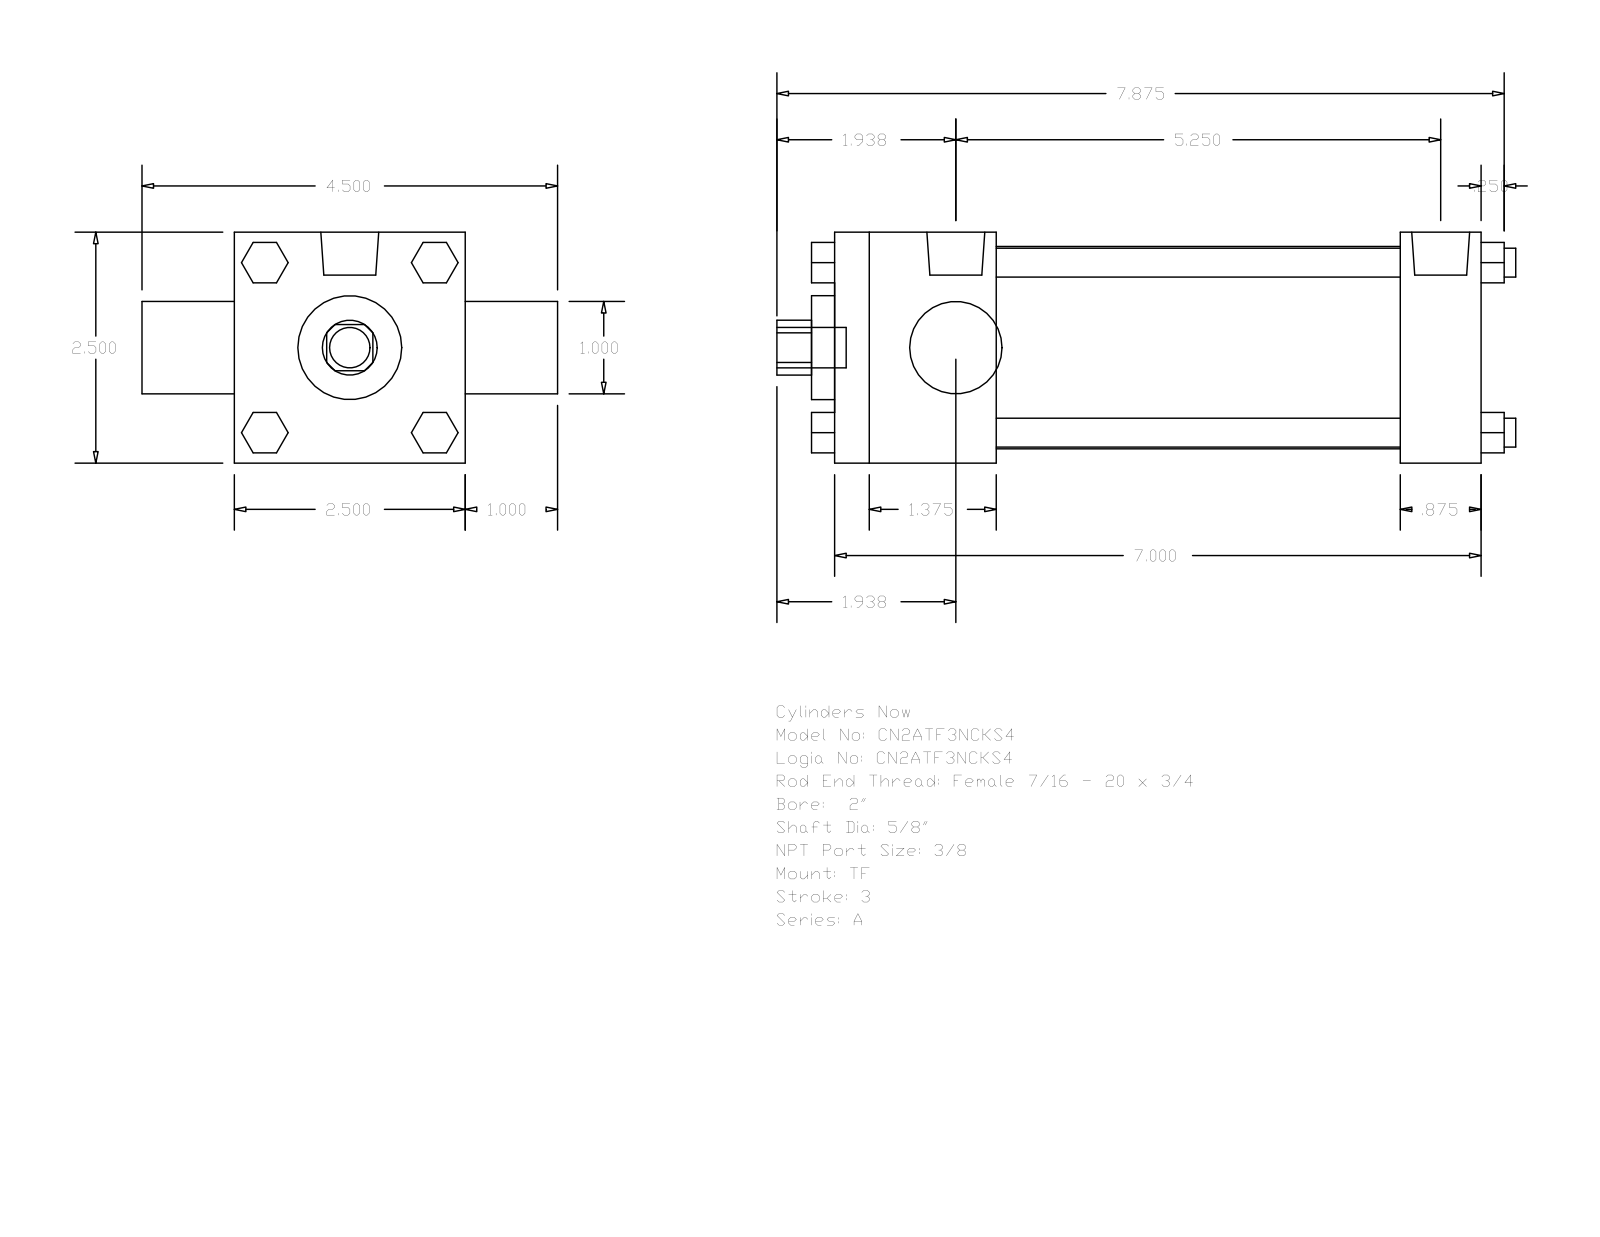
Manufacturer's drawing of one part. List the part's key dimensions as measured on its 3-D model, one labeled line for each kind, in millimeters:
Part name (STEP PRODUCT): A_TF__0200_0.625
STEP written by: GSSL Pune (CONFIG_CONTROL_DESIGN)
Units: millimetres
Bodies: 0 solids, 120 faces (92 planar, 28 cylindrical, 0 other)
Overall size (bounding box): 203.2 × 114.3 × 63.5
Round holes (diameter × count): ⌀15.88 ×1, ⌀25.4 ×1, ⌀28.57 ×1, ⌀55.63 ×1
Round bosses / shafts (diameter × count): ⌀7.94 ×4, ⌀5.56 ×3, ⌀15.93 ×2, ⌀11.11 ×1
Partial cylindrical surfaces — rounded edges, fillets, slot ends (radius × count): R7.54 ×1
Main face-to-face distances: 63.5, 177.8, 44.45, 155.57, 111.12, 133.35, 22.23, 25.4, 88.9, 184.15
